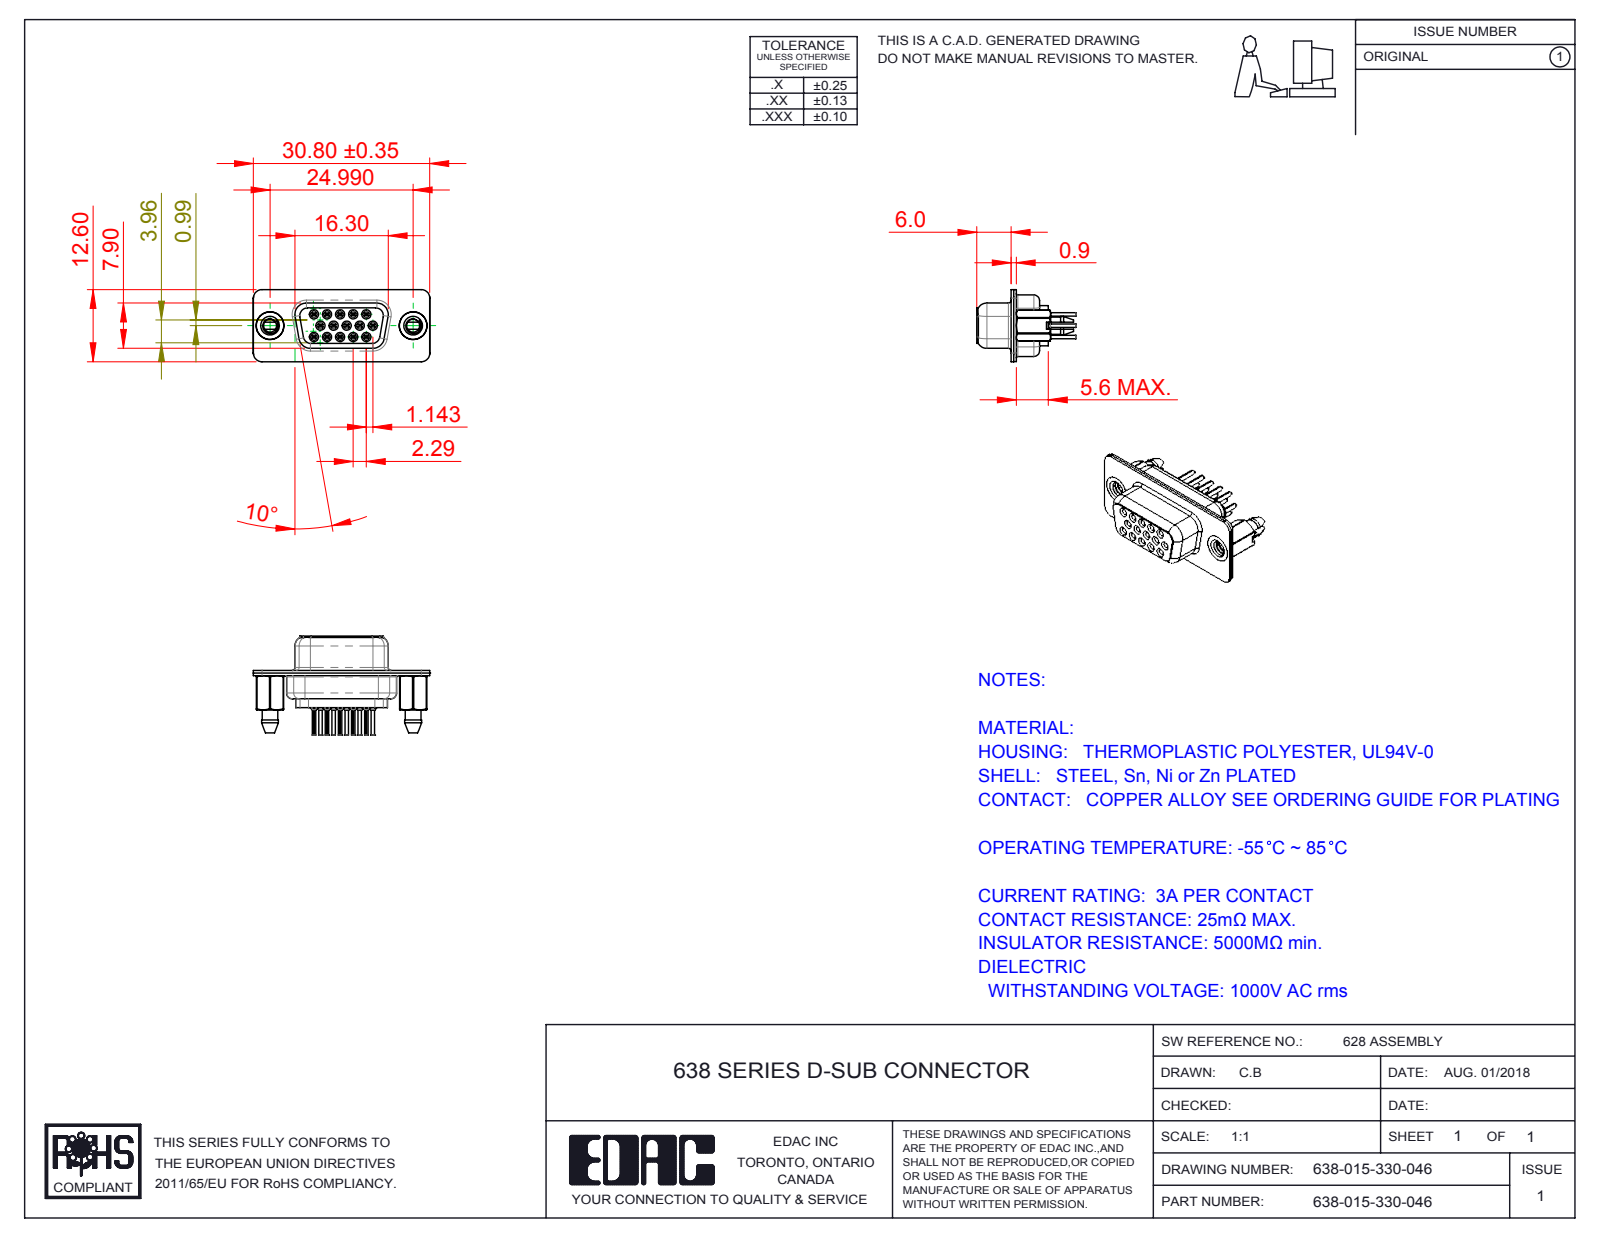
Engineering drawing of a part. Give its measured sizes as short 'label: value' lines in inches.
name: 638-015-330-046; 638 Contact Row 2_30L; 638 Contact Row 3_30L; 638 4-40 Threaded Boardlock_LP (+4 more)
written by: SolidWorks 2016 (CONFIG_CONTROL_DESIGN)
unit: in
bodies: 20 solids, 2258 faces (564 planar, 664 cylindrical, 1030 other)
size: 1.213 × 0.681 × 0.496
volume: 0.103 in³; area: 9.12 in²
holes: 15× ⌀0.008, 15× ⌀0.031, 15× ⌀0.039, 15× ⌀0.043, 15× ⌀0.063, 15× ⌀0.067, 15× ⌀0.071, 2× ⌀0.079, 2× ⌀0.089, 2× ⌀0.157, 2× ⌀0.159, 2× ⌀0.191
bosses: 15× ⌀0.079, 15× ⌀0.059, 15× ⌀0.047, 15× ⌀0.024, 2× ⌀0.195, 2× ⌀0.189
rounds: 30× R0.004, 22× R0.059, 12× R0.079, 10× R0.011, 8× R0.061, 5× R0.053, 4× R0.01, 4× R0.02
face distances: 0.018, 0.035, 0.016, 0.056, 0.35, 0.26, 0.055, 0.09, 0.236, 0.187
hole spacings: 0.156, 0.09, 0.18, 0.09, 0.238, 0.238, 0.27, 0.312
